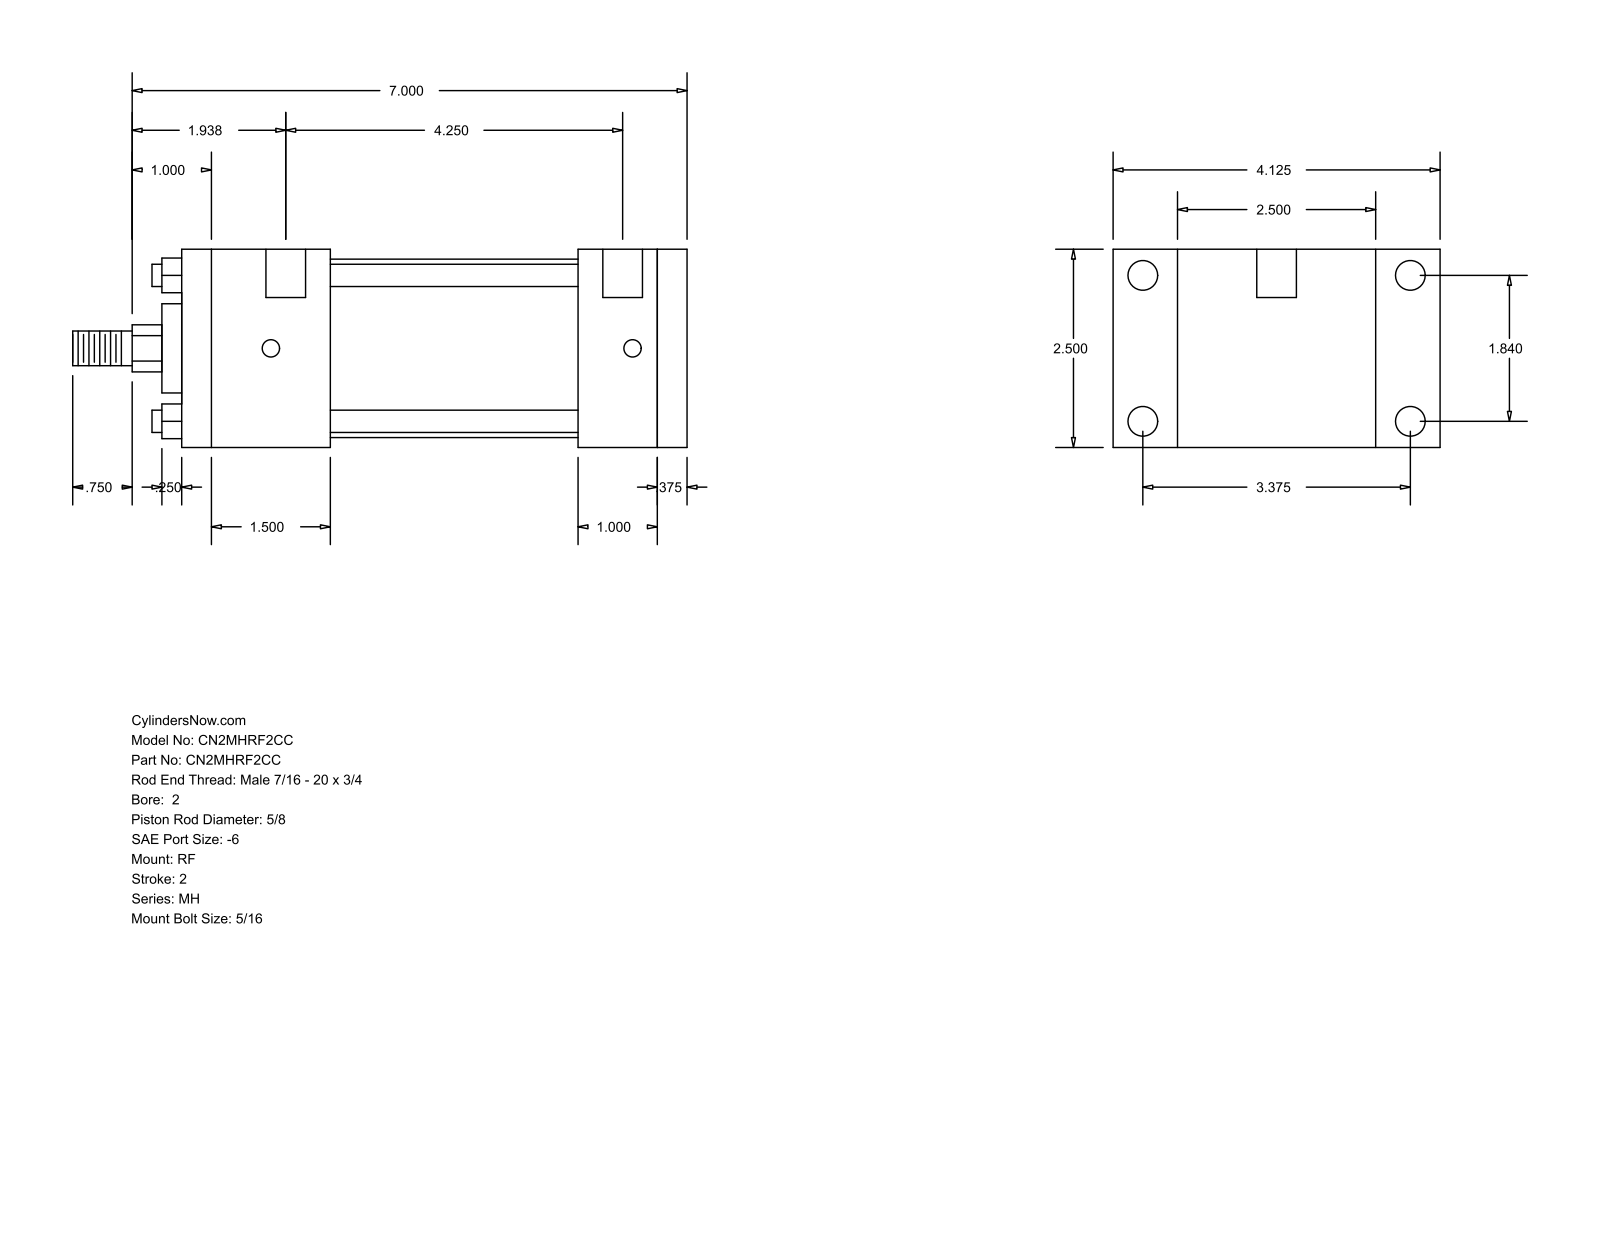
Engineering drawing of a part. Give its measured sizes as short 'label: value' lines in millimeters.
name: MH_RF__0200_0.625
written by: GSSL Pune (CONFIG_CONTROL_DESIGN)
unit: mm
bodies: 0 solids, 92 faces (64 planar, 28 cylindrical, 0 other)
size: 196.85 × 104.78 × 63.5
holes: 4× ⌀5.56, 4× ⌀9.53, 2× ⌀12.7
bosses: 4× ⌀7.14, 1× ⌀57.15, 1× ⌀28.57, 1× ⌀15.88, 1× ⌀11.11
rounds: 1× R7.54
face distances: 63.5, 161.92, 152.4, 9.52, 104.78, 25.4, 47.62, 127, 79.38, 114.3
hole spacings: 46.74, 85.72, 97.63, 115.89, 3.18, 4.76, 107.95, 111.13
